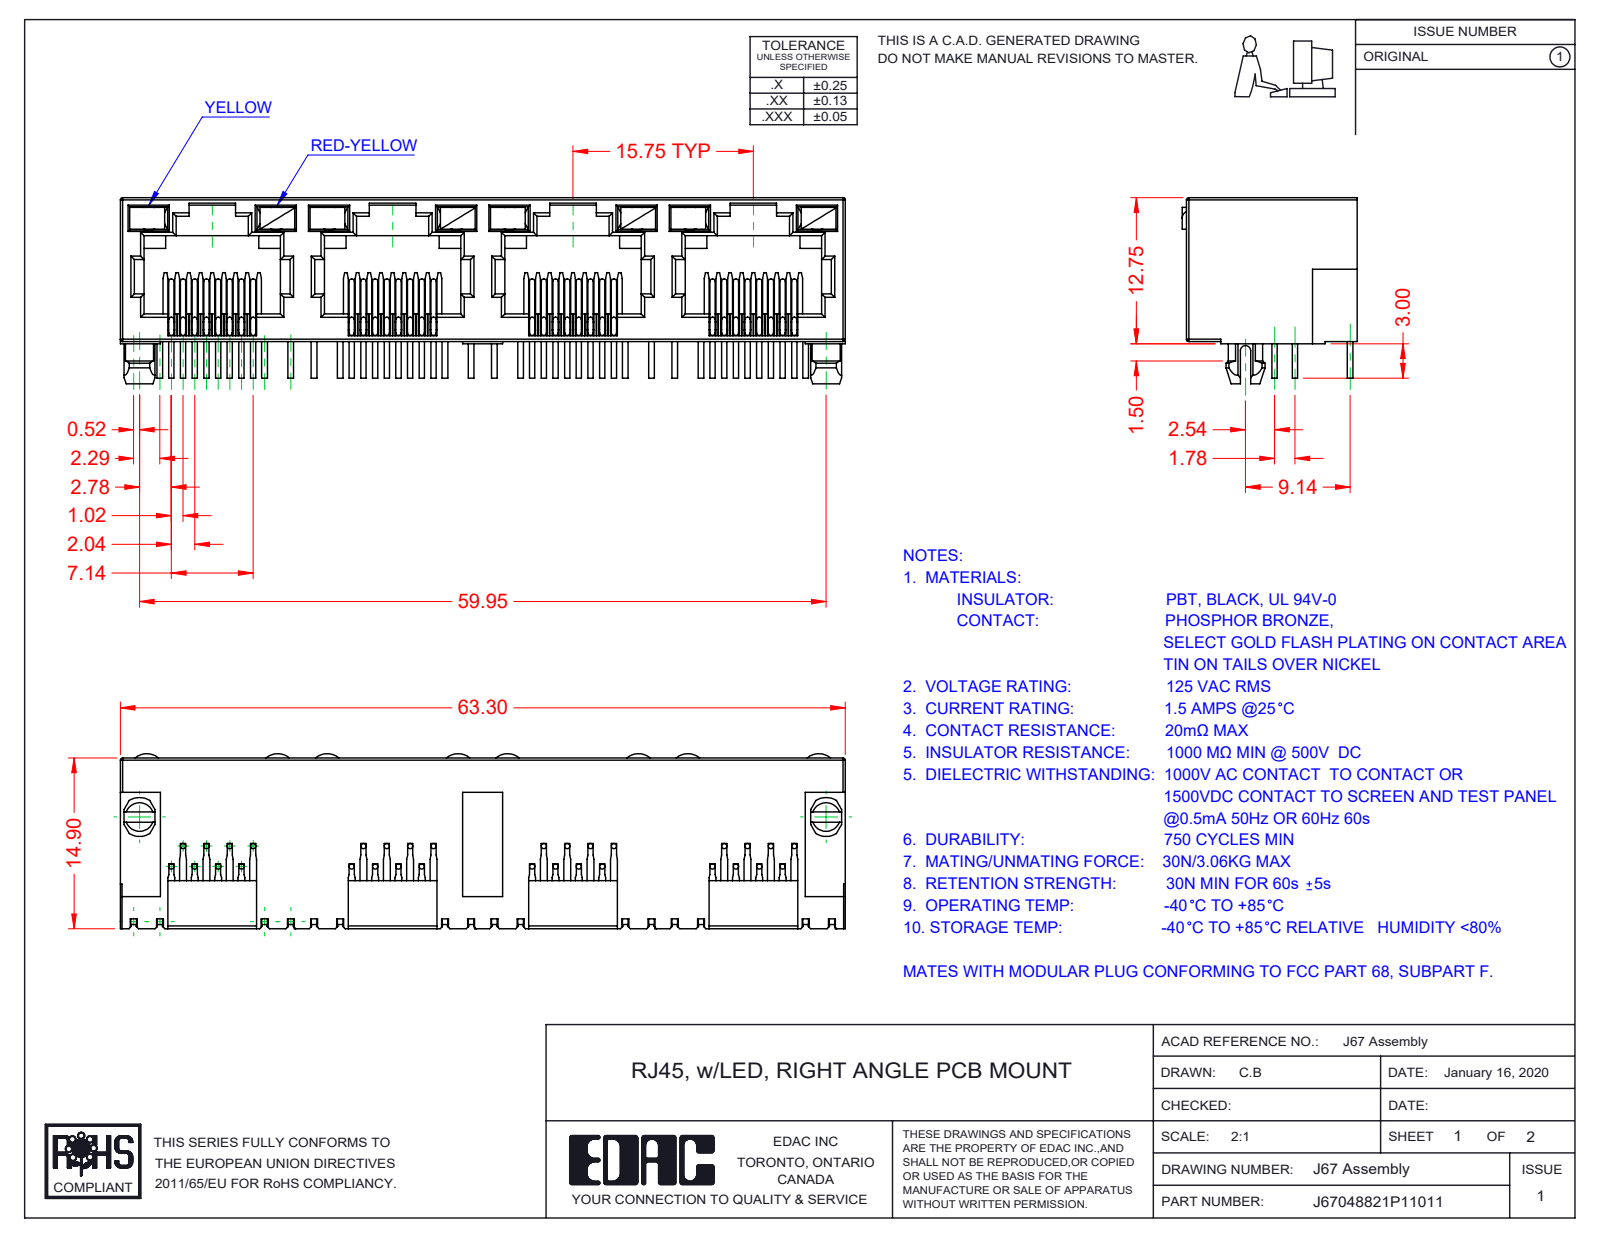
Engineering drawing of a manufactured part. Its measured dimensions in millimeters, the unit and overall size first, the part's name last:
Units: millimetres
Overall size (bounding box): 63.3 × 16.25 × 15.28
Round bosses / shafts (diameter × count): ⌀0.46 ×96
Partial cylindrical surfaces — rounded edges, fillets, slot ends (radius × count): R0.2 ×66, R0.3 ×29, R0.45 ×9, R1.55 ×8, R1.5 ×2, R1.7 ×2, R0.35 ×1, R1 ×1
Main face-to-face distances: 0.5, 12.55, 1.89, 0.89, 10, 15.75, 1, 1.39, 11, 11.89
Volume: 5 159 mm³ · Surface area: 11 573 mm²
Bodies: 41 solids, 2473 faces (1781 planar, 484 cylindrical, 208 other)
Part name (STEP PRODUCT): 67 Insulator; 67 LED RH_8-Red-Yellow; J67048822P18011; 67 LED LH_1-Yellow (+1 more)
STEP written by: SolidWorks 2016 (CONFIG_CONTROL_DESIGN)
